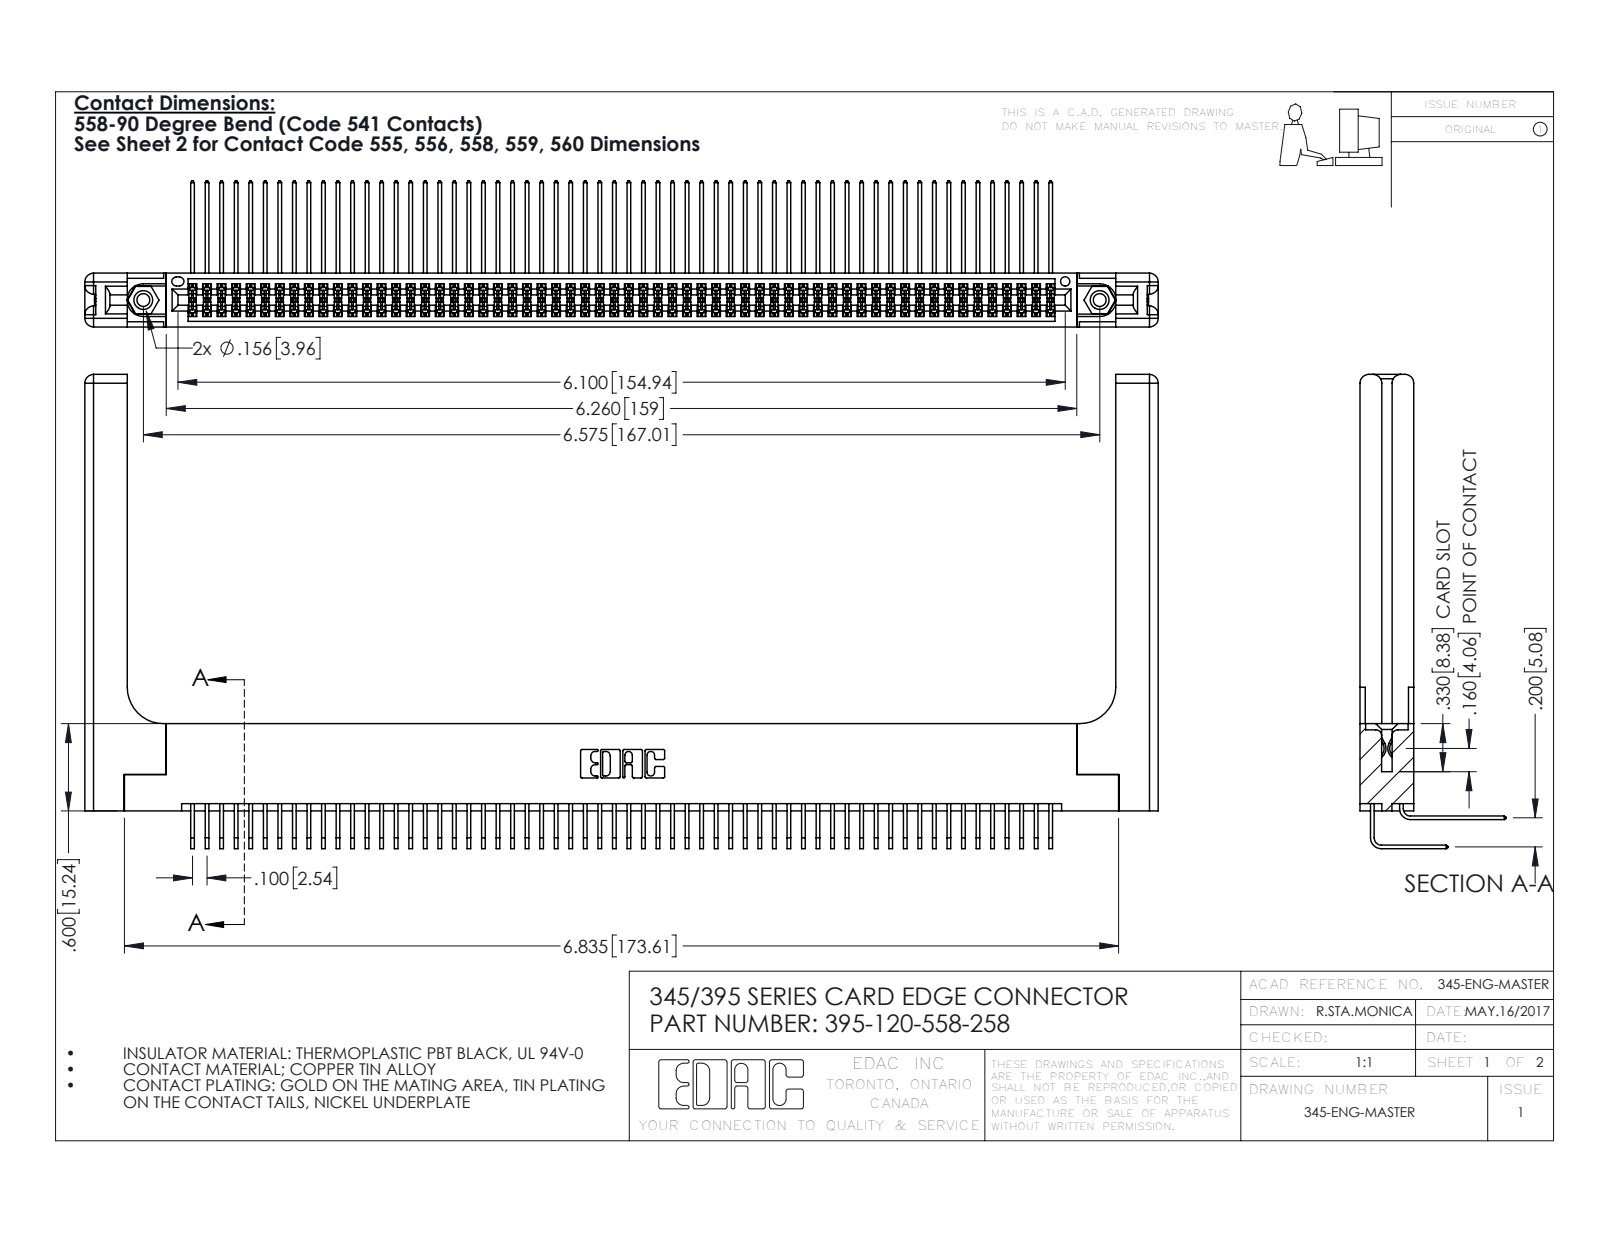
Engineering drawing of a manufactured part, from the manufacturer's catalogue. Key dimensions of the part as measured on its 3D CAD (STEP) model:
Part name (STEP PRODUCT): 345 Part_Flush Mounting Lugs - 0.156 Dia-TH; 345-292-001_558 Tail - 2; 395-120-558-258; 345-250-001_345-250-001-102 (+2 more)
STEP written by: SolidWorks 2016 (CONFIG_CONTROL_DESIGN)
Units: inches
Bodies: 125 solids, 6622 faces (4428 planar, 2134 cylindrical, 60 other)
Overall size (bounding box): 7.379 × 3.259 × 1.005
Volume: 1.681 in³ · Surface area: 57.11 in²
Round holes (diameter × count): ⌀0.089 ×2, ⌀0.125 ×2, ⌀0.156 ×2, ⌀0.064 ×1
Round bosses / shafts (diameter × count): ⌀0.155 ×2
Partial cylindrical surfaces — rounded edges, fillets, slot ends (radius × count): R0.006 ×181, R0.01 ×22, R0.06 ×16, R0.007 ×6, R0.031 ×6, R0.026 ×3, R0.014 ×2, R0.019 ×2
Main face-to-face distances: 0.072, 0.298, 0.2, 0.37, 0.098, 0.272, 0.025, 0.225, 0.148, 0.15
Hole centre spacings: 0.27, 6.339, 6.575
